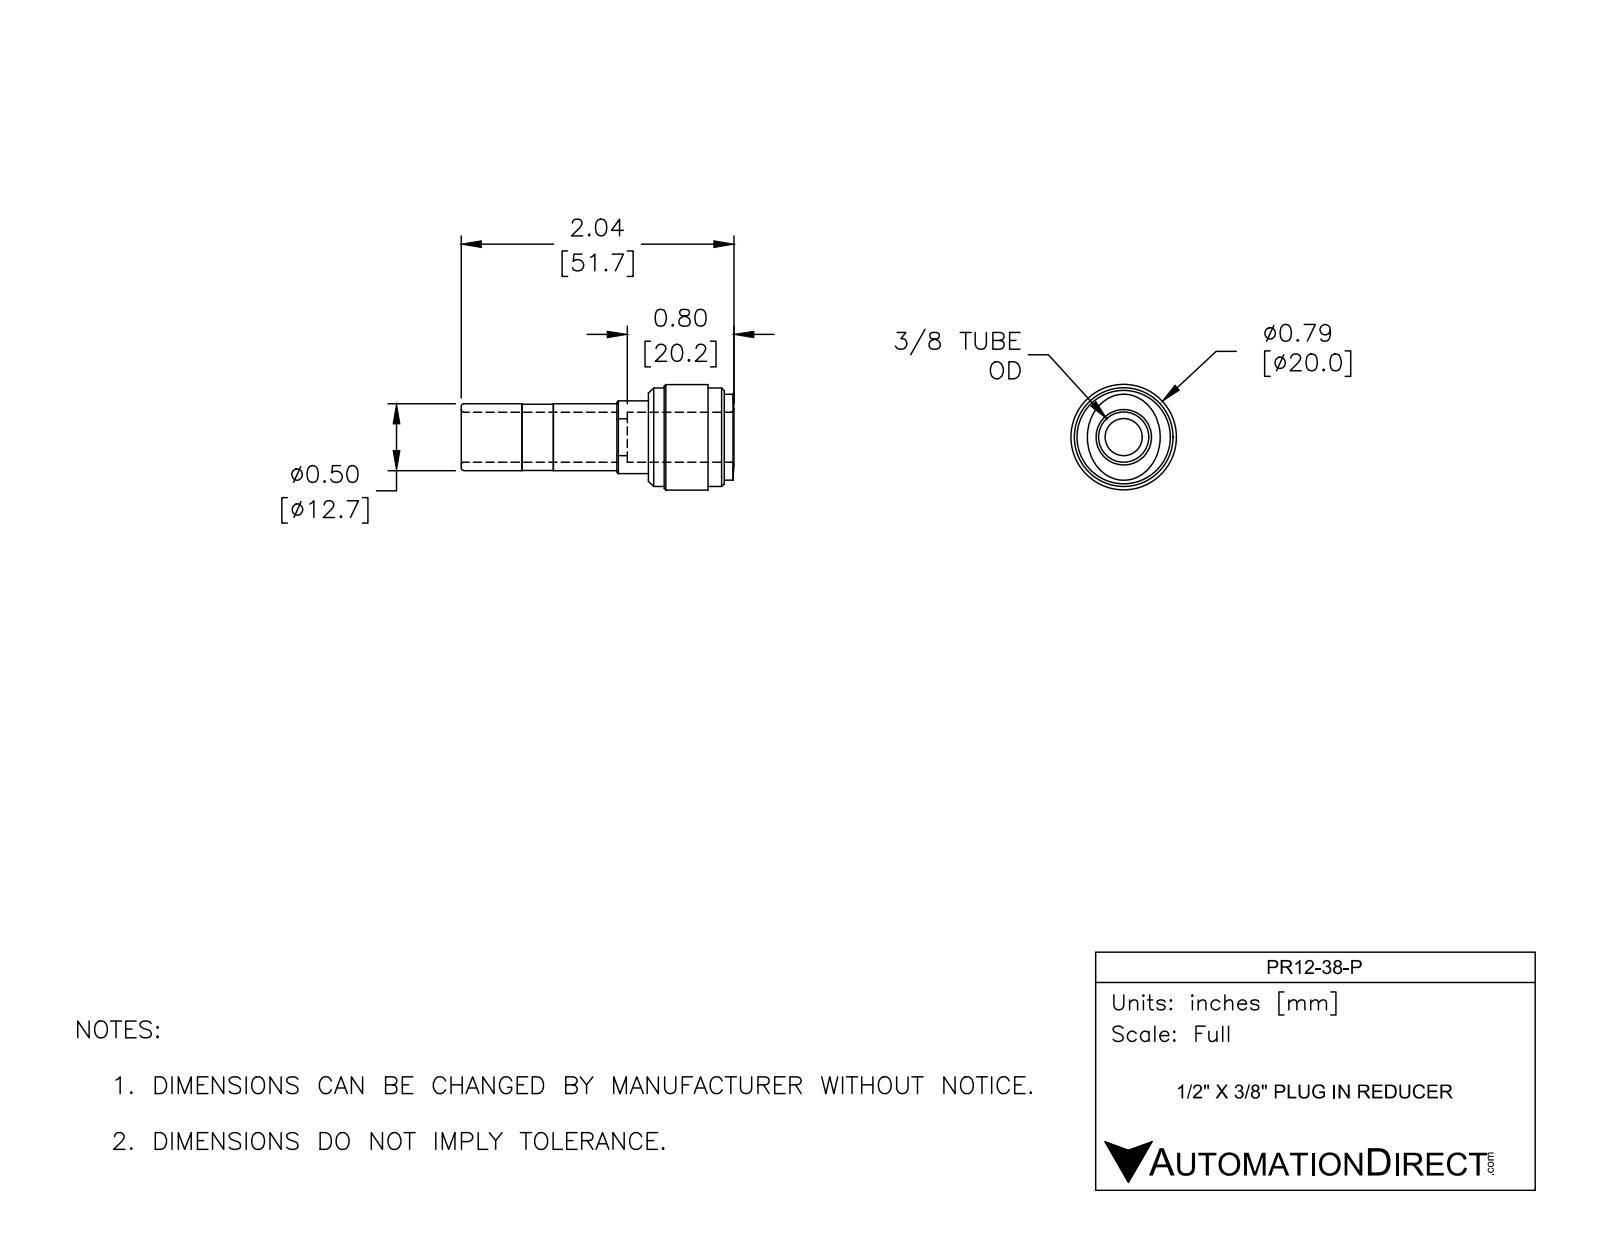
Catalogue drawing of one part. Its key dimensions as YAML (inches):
part_name: "PR12-38-P"
step_written_by: "SolidWorks 2017 (AUTOMOTIVE_DESIGN)"
units: inches
bodies: {solids: 1, faces: 50, planar: 8, cylindrical: 20, other: 22}
overall_size: [2.036, 0.787, 0.787]
volume: 0.34
surface_area: 6.791
round_holes:
  - {diameter: 0.276, count: 1}
  - {diameter: 0.374, count: 1}
round_bosses_or_shafts:
  - {diameter: 0.787, count: 1}
  - {diameter: 0.736, count: 1}
  - {diameter: 0.543, count: 1}
  - {diameter: 0.5, count: 1}
  - {diameter: 0.494, count: 1}
face_to_face_distances: [0.567, 0.236, 0.803, 0.681, 0.445, 0.122, 0.079, 0.157, 0.602, 0.724]
